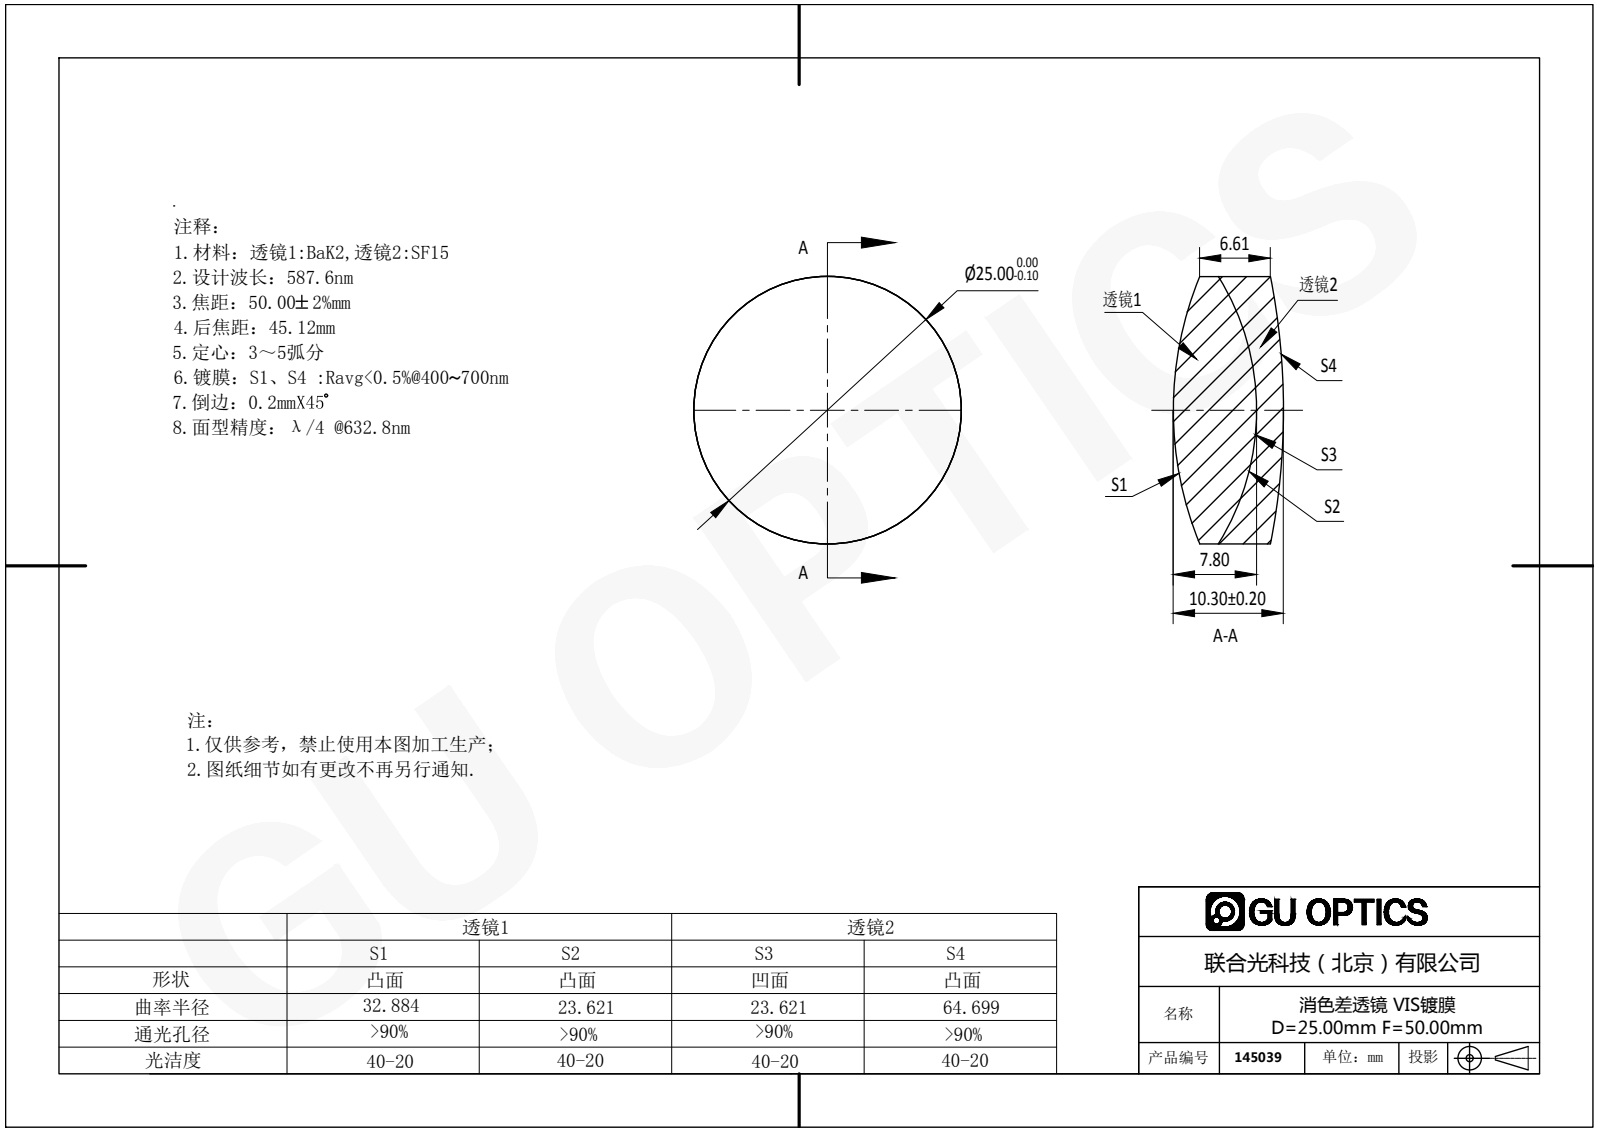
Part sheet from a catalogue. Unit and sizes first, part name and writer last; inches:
Units: inches
Overall size (bounding box): 0.984 × 0.984 × 0.406
Round bosses / shafts (diameter × count): ⌀0.984 ×1
Volume: 0.254 in³ · Surface area: 4.01 in²
Bodies: 2 solids, 12 faces (0 planar, 4 cylindrical, 8 other)
Part name (STEP PRODUCT): 145039
STEP written by: SolidWorks 2016 (AUTOMOTIVE_DESIGN)
